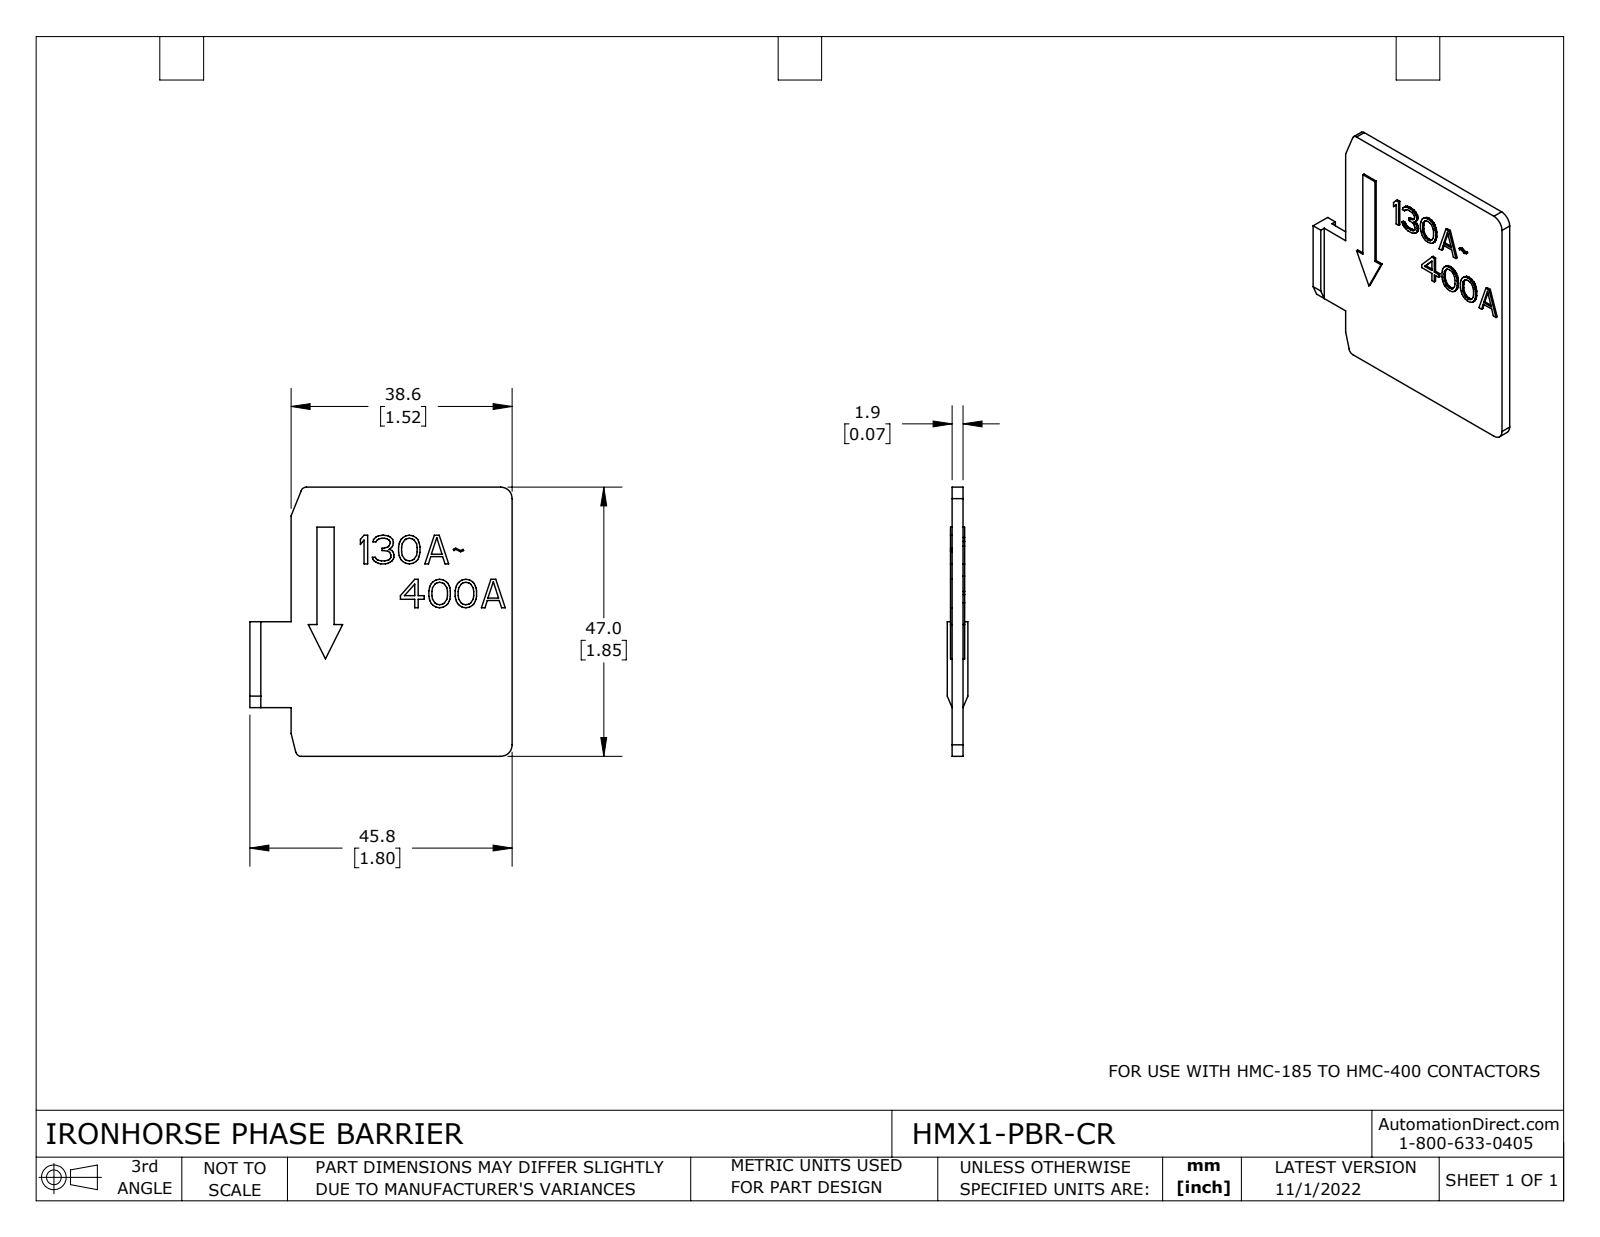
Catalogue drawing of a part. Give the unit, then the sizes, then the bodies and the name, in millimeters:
Units: millimetres
Overall size (bounding box): 47 × 45.79 × 3.6
Partial cylindrical surfaces — rounded edges, fillets, slot ends (radius × count): R1 ×2, R2 ×2
Main face-to-face distances: 1.9, 2.2, 2.5, 47, 45.79, 0.85, 3.05, 0.55, 2.75, 7.2
Volume: 3 749 mm³ · Surface area: 4 363 mm²
Bodies: 1 solid, 548 faces (544 planar, 4 cylindrical, 0 other)
Part name (STEP PRODUCT): HMX1-PBR-CR
STEP written by: SolidWorks 2021 (CONFIG_CONTROL_DESIGN)
